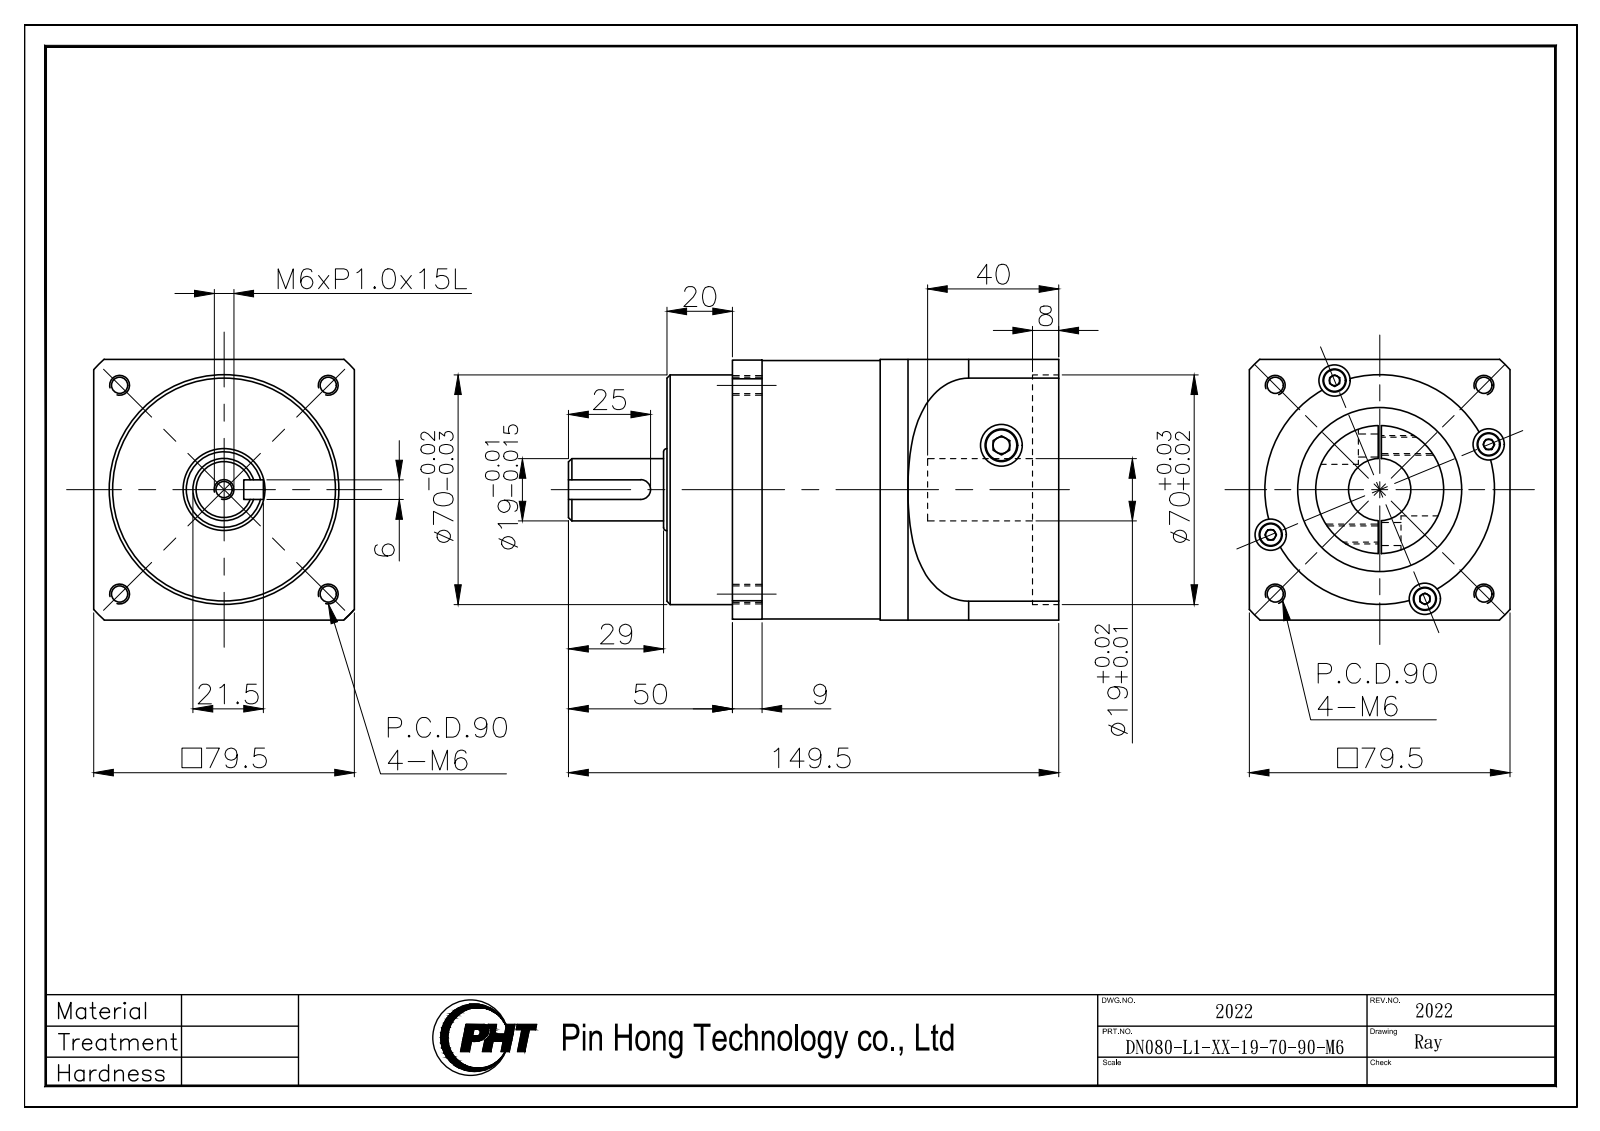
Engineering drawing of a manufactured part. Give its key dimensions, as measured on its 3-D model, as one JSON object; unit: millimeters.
{"part_name": "DN080-L1-XX-19-70-90-M6_2022", "step_written_by": "SolidWorks 2016 (AUTOMOTIVE_DESIGN)", "units": "millimeters", "bodies": {"solids": 1, "faces": 184, "planar": 74, "cylindrical": 79, "other": 31}, "overall_size": [149.5, 79.5, 79.5], "volume_mm3": 562878, "surface_area_mm2": 71019, "round_holes": [[5, 5], [5.5, 4], [9.5, 4], [12.7, 2], [19, 1], [50, 1], [70, 1]], "round_bosses_or_shafts": [[8.5, 4], [79, 1], [78.8, 1], [39, 1], [25, 1]], "partial_cylinders_radius": [[3, 1], [54, 1]], "face_to_face_distances": [79.5, 29, 20, 99.5, 119.5, 111.5, 8, 91.5, 82.5, 90.5], "hole_center_spacings": [18.1, 36, 45, 45.62, 50.91, 63.64, 67.53, 79.47]}
